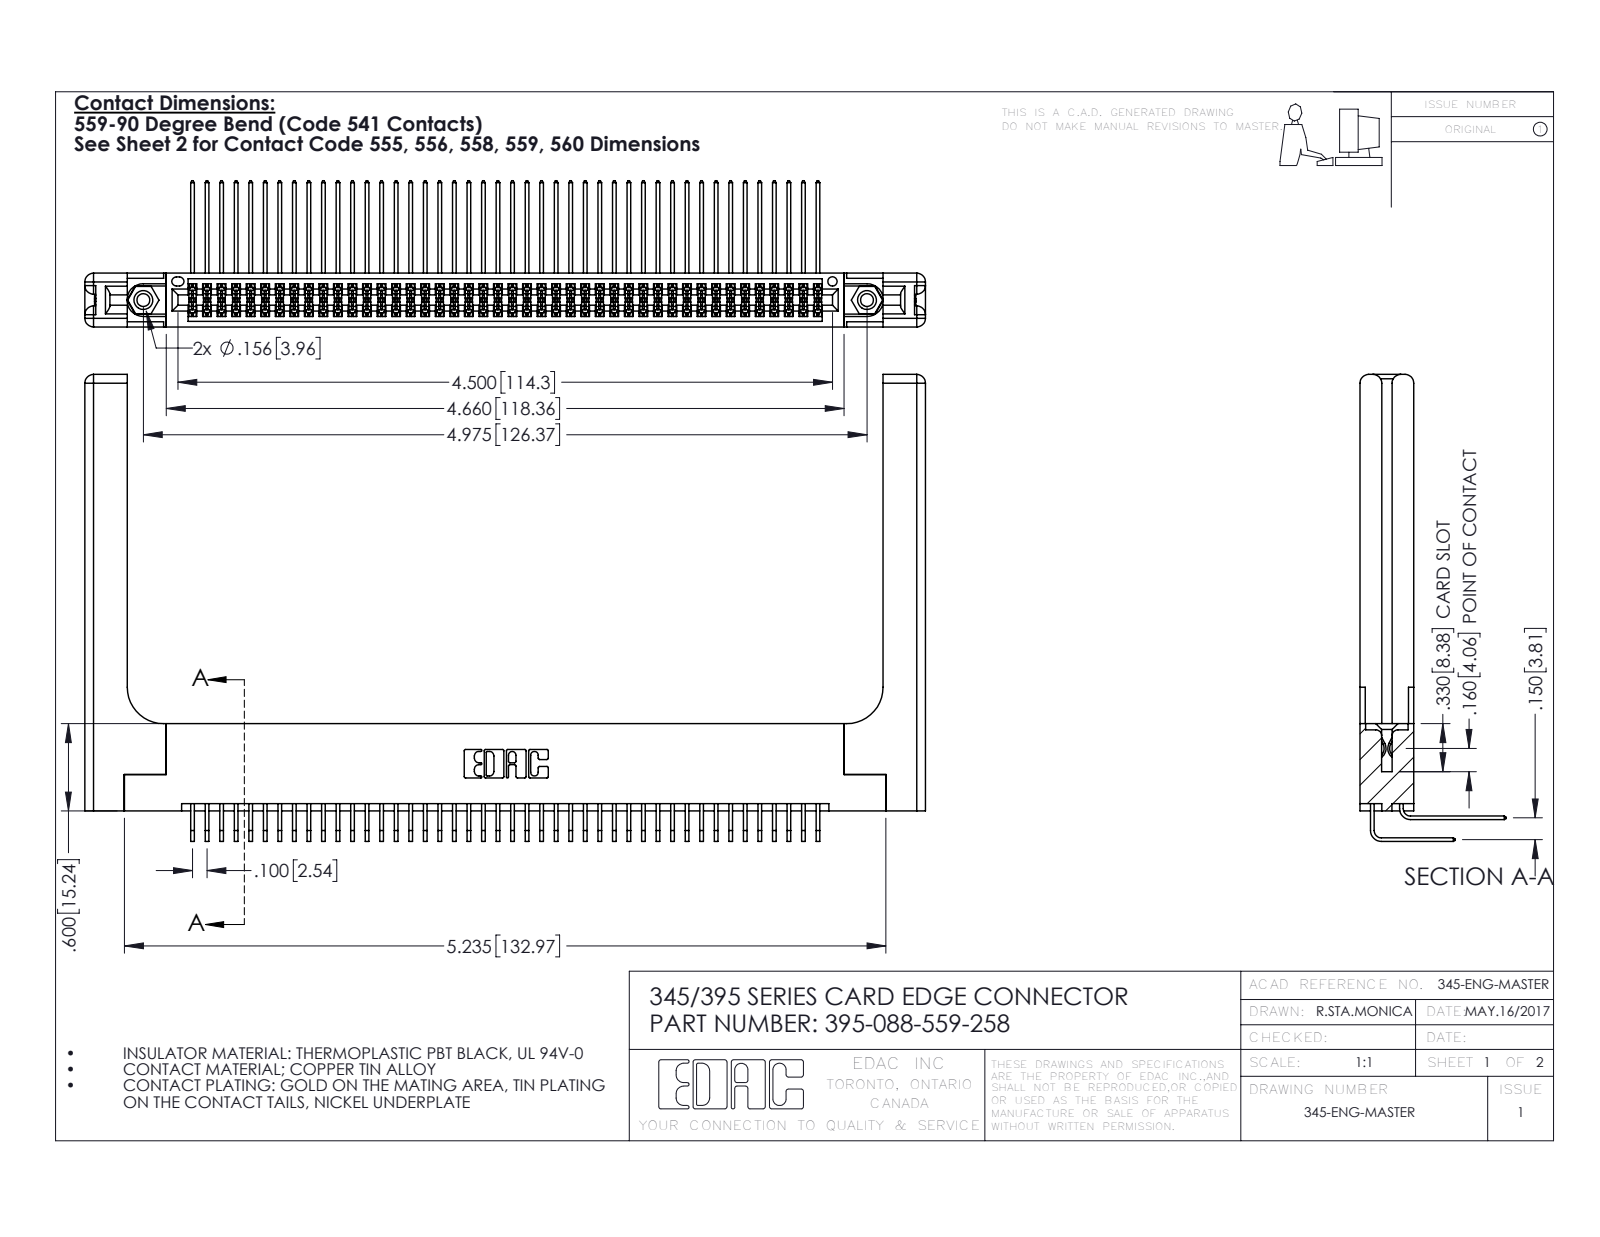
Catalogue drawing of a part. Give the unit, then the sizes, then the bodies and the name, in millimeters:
Units: millimetres
Overall size (bounding box): 146.8 × 81.5 × 25.5
Round holes (diameter × count): ⌀2.3 ×2, ⌀3.2 ×2, ⌀4 ×2, ⌀1.6 ×1
Round bosses / shafts (diameter × count): ⌀3.9 ×2
Partial cylindrical surfaces — rounded edges, fillets, slot ends (radius × count): R0.2 ×133, R0.3 ×22, R1.5 ×16, R0.2 ×6, R0.8 ×6, R0.7 ×3, R0.4 ×2, R0.5 ×2
Main face-to-face distances: 1.8, 7.6, 9.4, 5.1, 2.5, 6.9, 0.6, 5.7, 4.4, 3.8
Hole centre spacings: 6.9, 120.4, 126.4
Volume: 23 250 mm³ · Surface area: 29 340 mm²
Bodies: 93 solids, 4958 faces (3308 planar, 1590 cylindrical, 60 other)
Part name (STEP PRODUCT): 395-088-559-258; 345-292-001_559 Tail - 2; 345-292-001_558 559 Tail - 1; 345 Part_Flush Mounting Lugs - 0.156 Dia-TH (+2 more)
STEP written by: SolidWorks 2016 (CONFIG_CONTROL_DESIGN)
